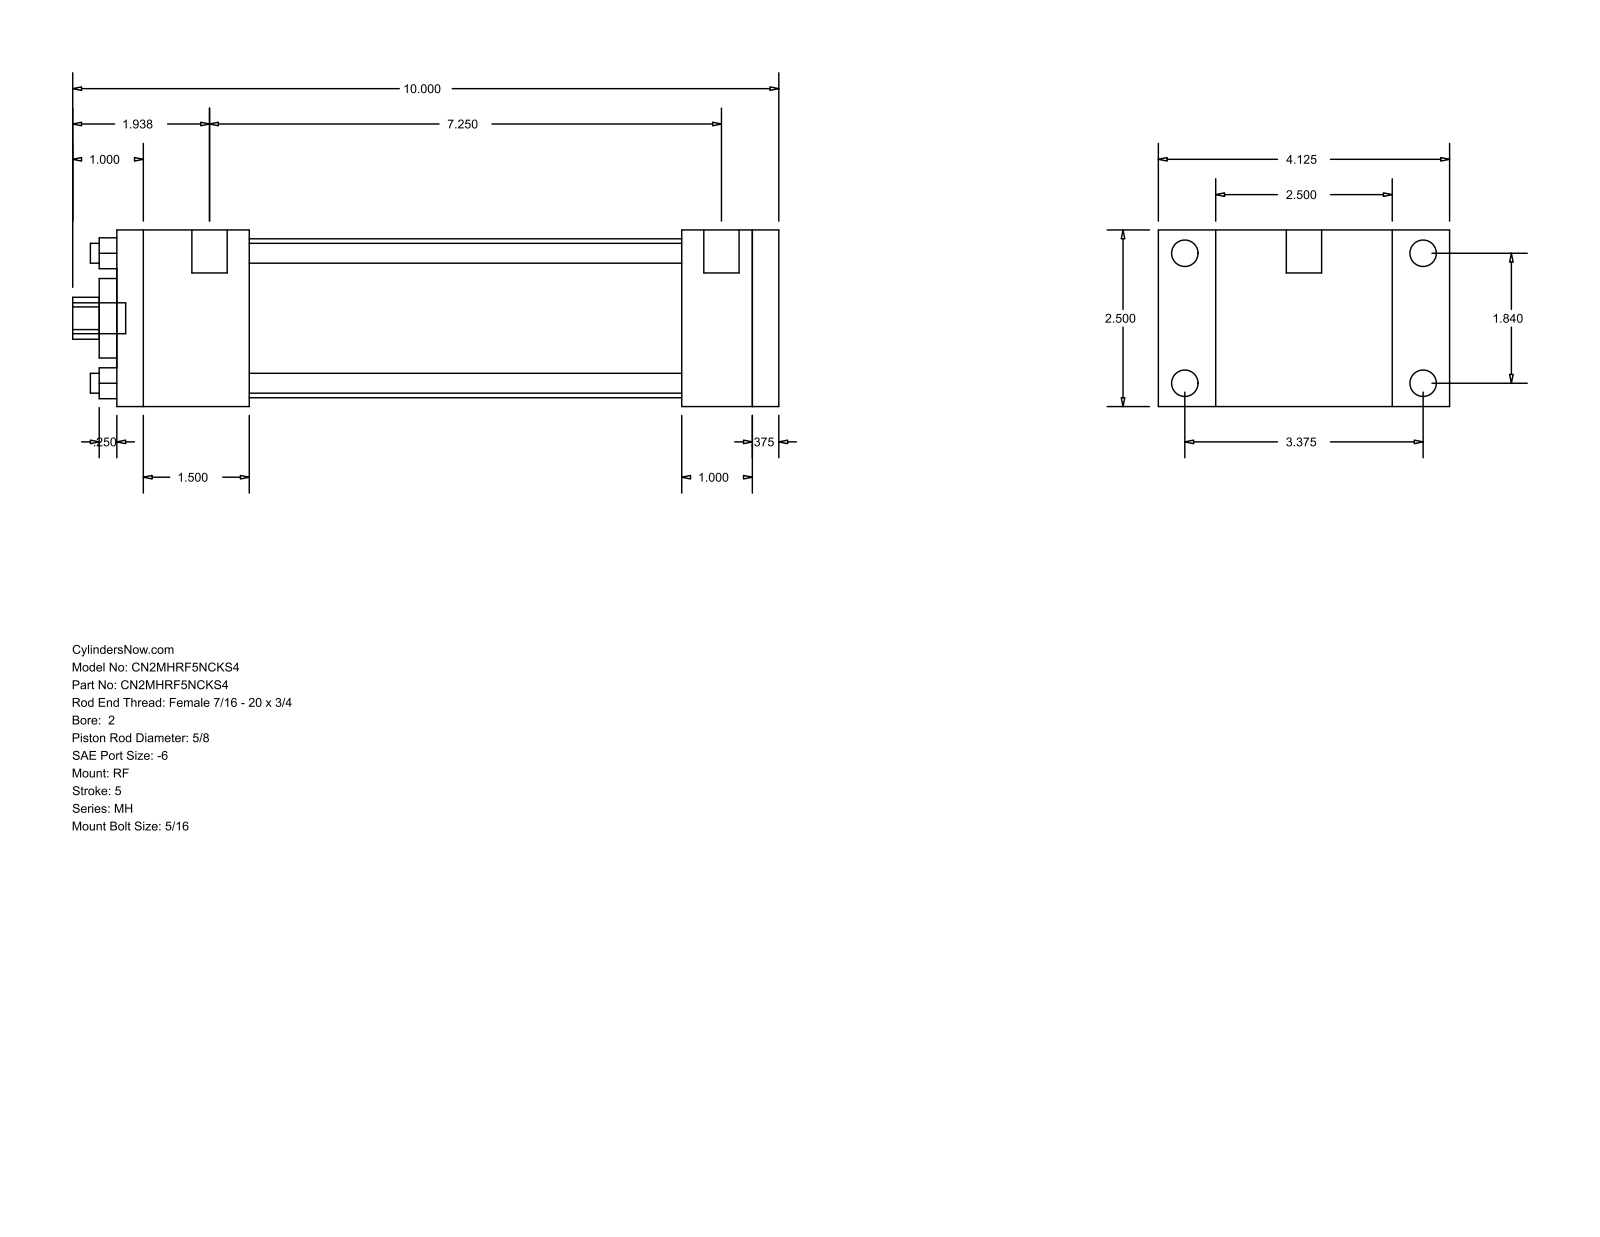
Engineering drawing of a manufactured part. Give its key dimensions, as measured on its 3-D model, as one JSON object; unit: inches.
{"part_name": "MH_RF__0200_0.625", "step_written_by": "GSSL Pune (CONFIG_CONTROL_DESIGN)", "units": "inches", "bodies": {"solids": 0, "faces": 92, "planar": 64, "cylindrical": 28, "other": 0}, "overall_size": [10, 4.125, 2.5], "round_holes": [[0.281, 4], [0.625, 1], [1.125, 1], [2.25, 1]], "round_bosses_or_shafts": [[0.375, 4], [0.219, 4], [0.5, 2], [0.437, 1]], "partial_cylinders_radius": [[0.297, 1]], "face_to_face_distances": [2.5, 9.375, 0.375, 9, 1, 1.875, 8, 6.125, 7.125, 7.5], "hole_center_spacings": [1.301, 1.84, 2.602]}
